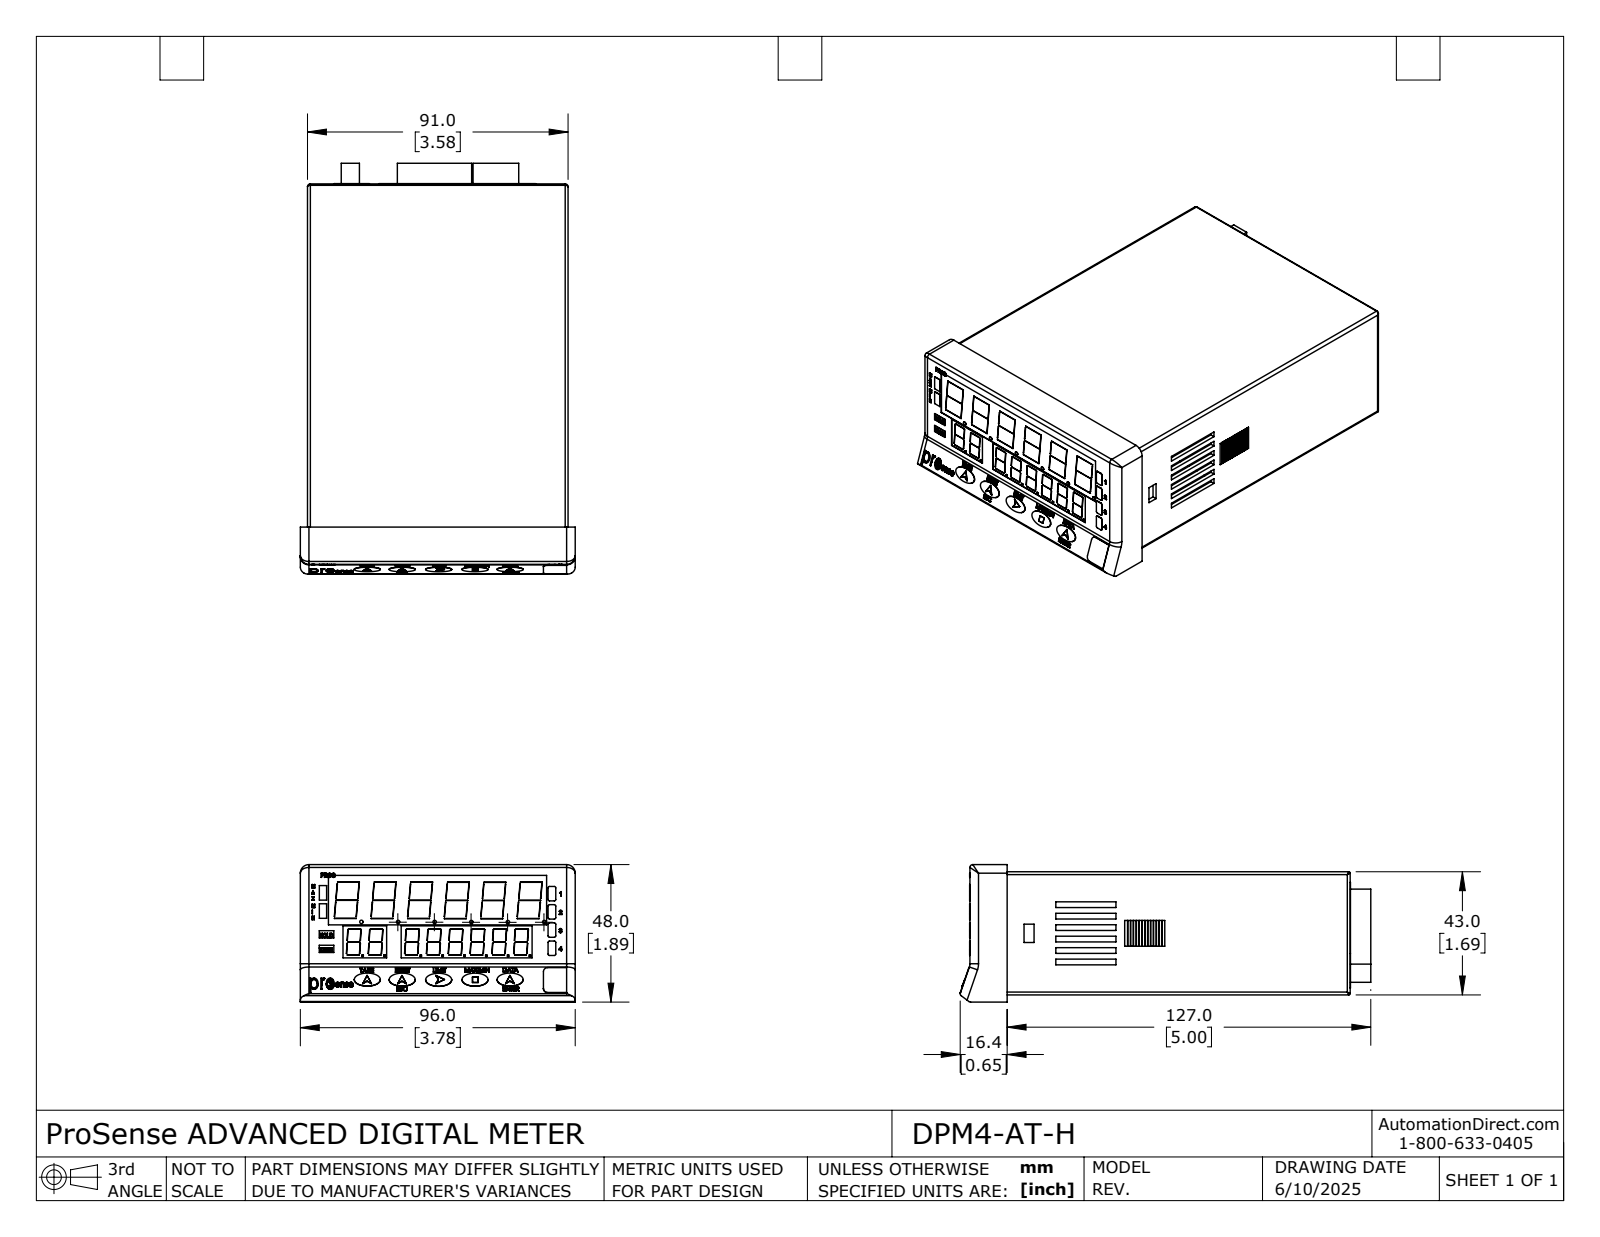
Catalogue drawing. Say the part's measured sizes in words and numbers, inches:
The part is named "DPM4-AT-H". Its 3-D file was written by "SolidWorks 2024 (AUTOMOTIVE_DESIGN)". It is 11 solids with 2017 faces: 1686 planar, 79 cylindrical and 252 other. Overall it measures 5.647 by 3.78 by 1.89 inches. Its volume is 18.98 cubic inches and its surface area 112.5 square inches. Round bosses or shafts: 14 of diameter 0.078, 6 of diameter 0.047. Partial cylindrical surfaces (rounded edges, fillets, slot ends): 18 of radius 0.02, 8 of radius 0.039, 6 of radius 0.118, 2 of radius 0.004, 2 of radius 0.059, 1 of radius 0.03, 1 of radius 0.138, 1 of radius 0.197. The main face-to-face distances are 0.059, 1.693, 1.634, 0.098, 3.583, 1.575, 1.732, 3.524, 0.157, 2.823.
